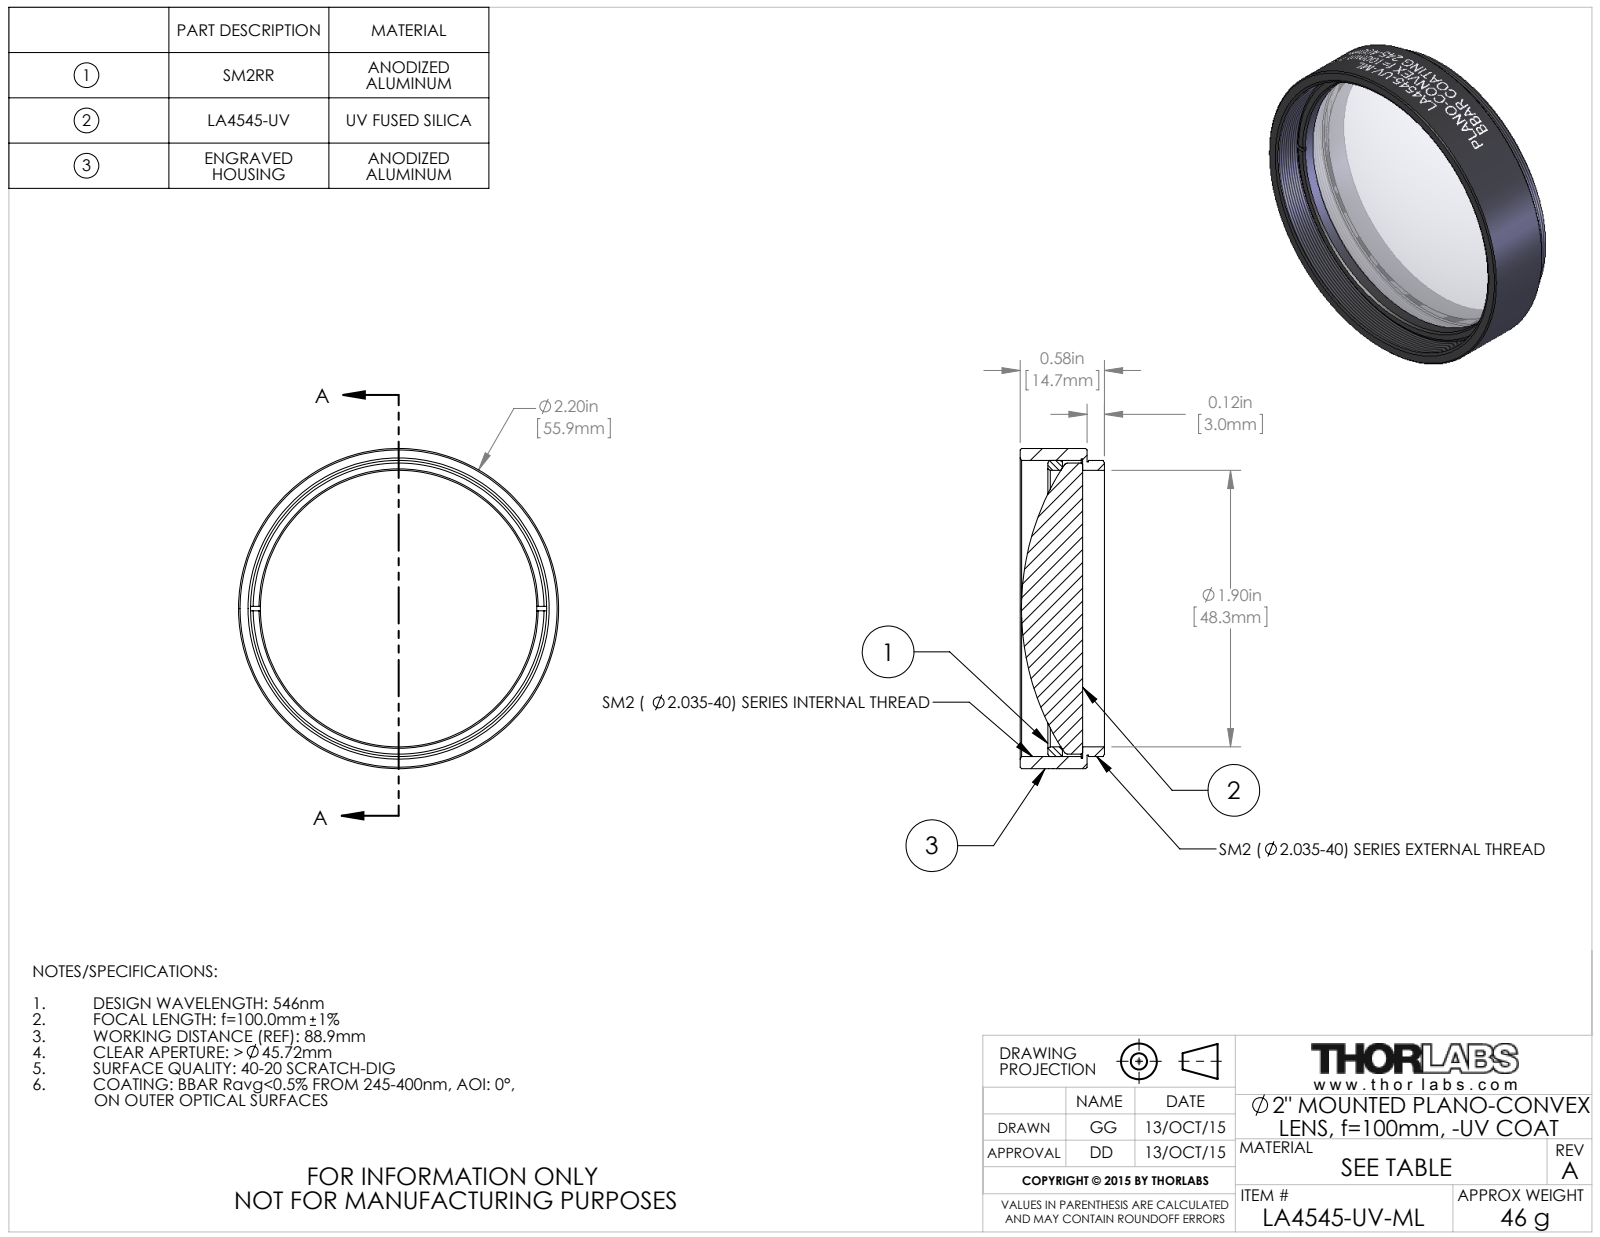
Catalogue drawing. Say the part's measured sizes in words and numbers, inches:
The part is named "TTN039306-E0W". Its 3-D file was written by "SolidWorks 2014 (CONFIG_CONTROL_DESIGN)". It is 3 solids with 148 faces: 16 planar, 108 cylindrical and 24 other. Overall it measures 2.2 by 2.2 by 0.58 inches. Its volume is 1.212 cubic inches and its surface area 18.76 square inches. Round holes: 1 of diameter 1.9, 1 of diameter 2.055. Round bosses or shafts: 1 of diameter 2.2, 1 of diameter 2.035, 1 of diameter 2.015, 1 of diameter 2. The main face-to-face distances are 0.03, 0.46, 0.43, 0.12, 0.15, 0.58, 0.291, 0.17, 0.141, 0.29.
